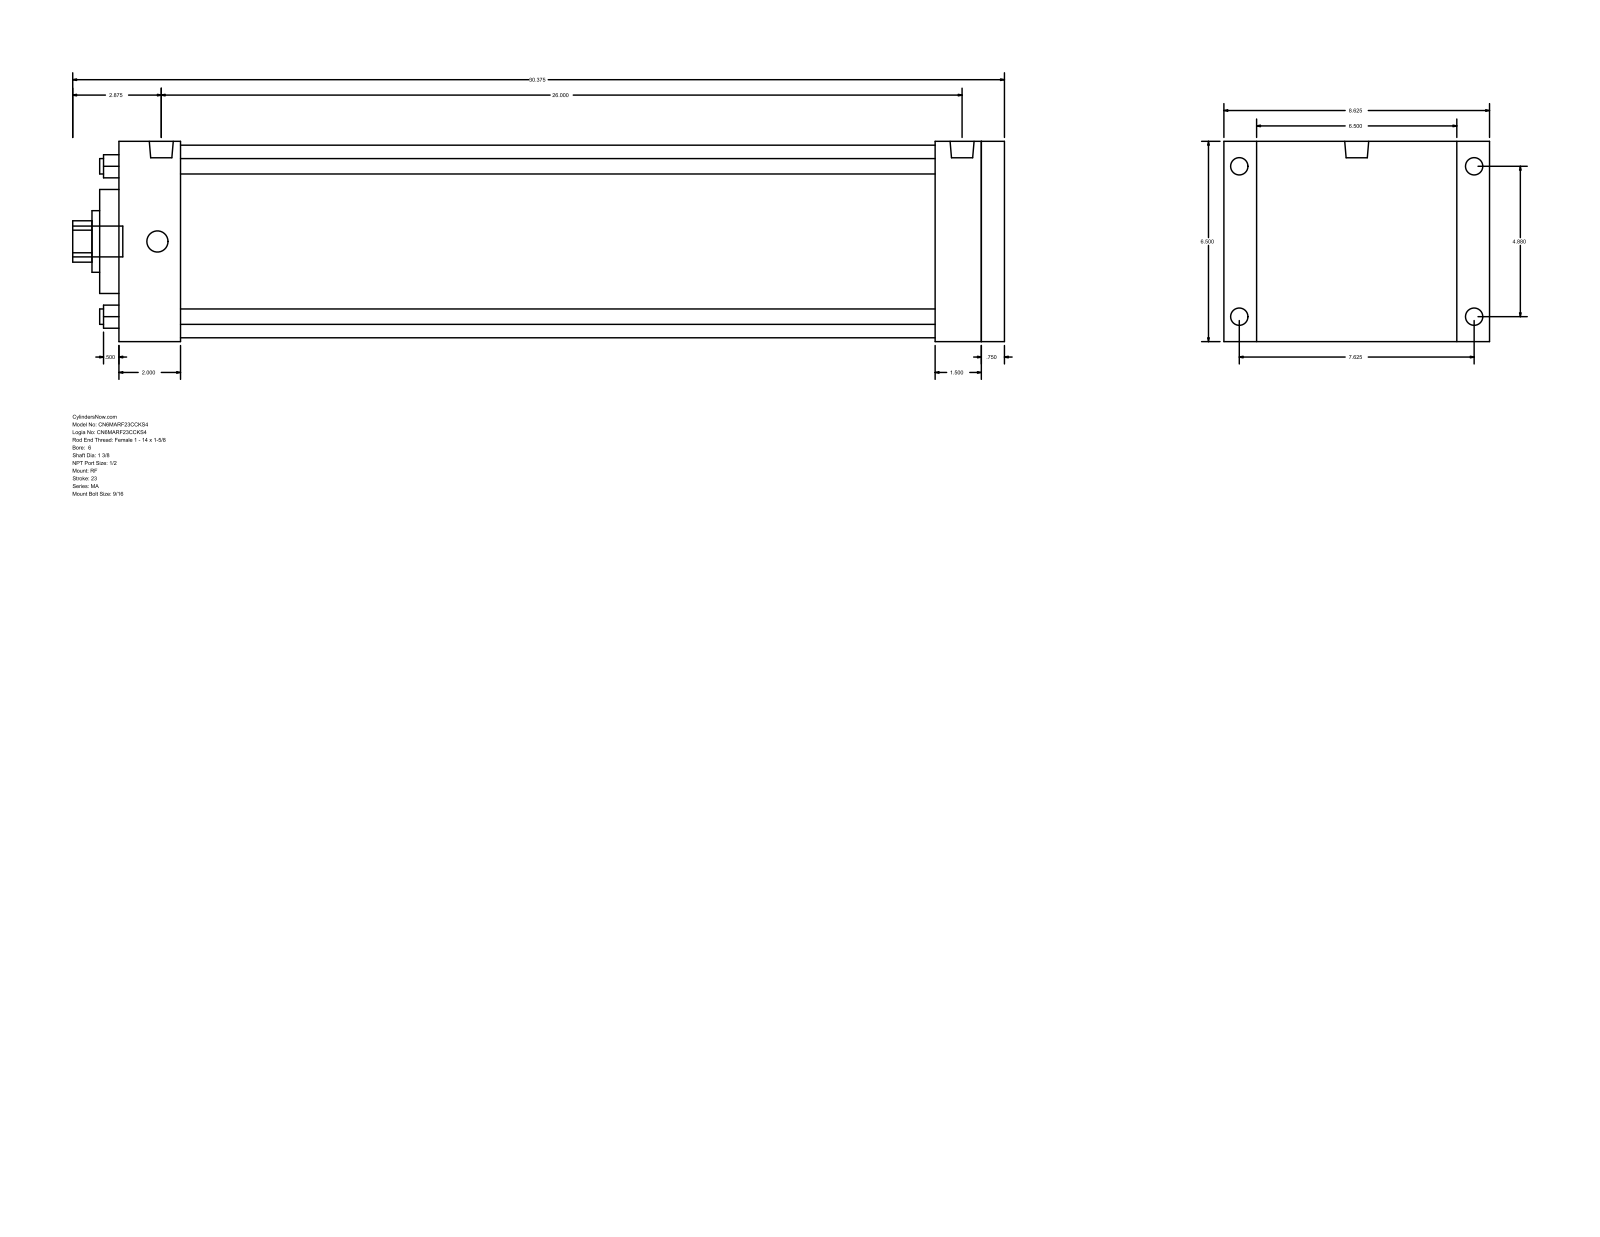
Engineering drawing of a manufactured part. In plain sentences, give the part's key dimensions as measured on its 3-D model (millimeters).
The part is named "MA_RF__0600_1.375". Its 3-D file was written by "GSSL Pune (CONFIG_CONTROL_DESIGN)". It is 0 solids with 94 faces: 65 planar, 29 cylindrical and 0 other. Overall it measures 771.52 by 219.07 by 165.1 millimeters. Round holes: 4 of diameter 12.7, 1 of diameter 34.92, 1 of diameter 50.8, 1 of diameter 85.72, 1 of diameter 158.75. Round bosses or shafts: 4 of diameter 17.46, 4 of diameter 14.29, 2 of diameter 19.77, 1 of diameter 25.4. Partial cylindrical surfaces (rounded edges, fillets, slot ends): 1 of radius 17.06. The main face-to-face distances are 165.1, 733.42, 19.04, 714.38, 38.1, 50.8, 663.58, 682.62, 676.28, 625.48. The hole center spacings are 87.65, 123.96, 175.31.
